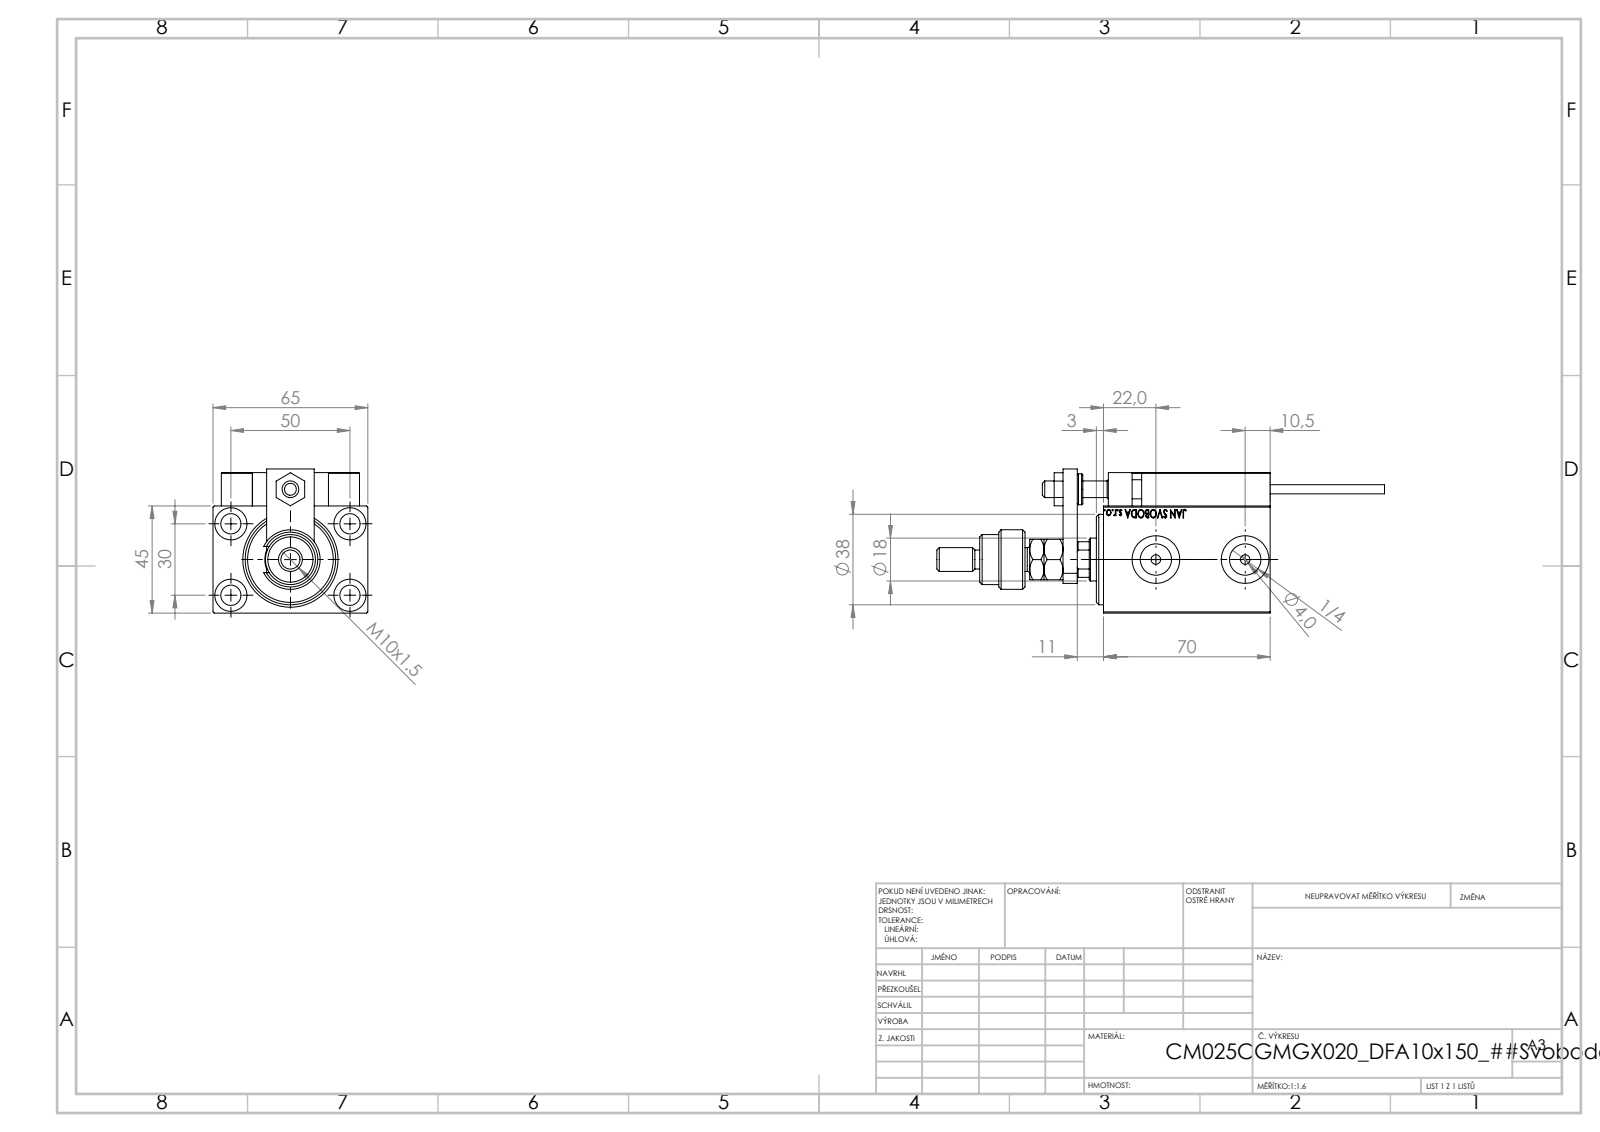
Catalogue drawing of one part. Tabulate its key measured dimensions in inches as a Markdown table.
| quantity | value |
| --- | --- |
| part name | SWITCH_X_FRONT_BACK; SWITCH X; V450CM_VC_B; MAGNET (+8 more) |
| STEP written by | SolidWorks 2019 (CONFIG_CONTROL_DESIGN) |
| units | inches |
| bodies | 25 solids, 1367 faces (588 planar, 201 cylindrical, 578 other) |
| overall size | 7.402 × 2.559 × 2.382 |
| volume | 14.33 in³ |
| surface area | 115.7 in² |
| round holes (diameter × count) | 0.157 × 6, 0.315 × 5, 0.335 × 5, 0.126 × 4, 0.531 × 4, 0.197 × 2, 0.518 × 2, 0.787 × 2, 0.276 × 1, 0.571 × 1, 0.709 × 1, 0.846 × 1 |
| round bosses / shafts (diameter × count) | 0.197 × 2, 0.15 × 2, 0.984 × 1, 0.827 × 1, 0.63 × 1, 0.512 × 1, 0.433 × 1, 0.394 × 1 |
| partial cylindrical surfaces (radius × count) | 0.012 × 30, 0.118 × 2, 0.217 × 1, 0.335 × 1, 0.344 × 1 |
| main face-to-face distances | 1.772, 2.323, 0.551, 2.559, 0.236, 0.118, 0.748, 0.276, 0.197, 0.866 |
| hole center spacings | 1.148, 0.448, 0.787, 0.87, 1.138, 1.165, 1.169, 1.181 |
